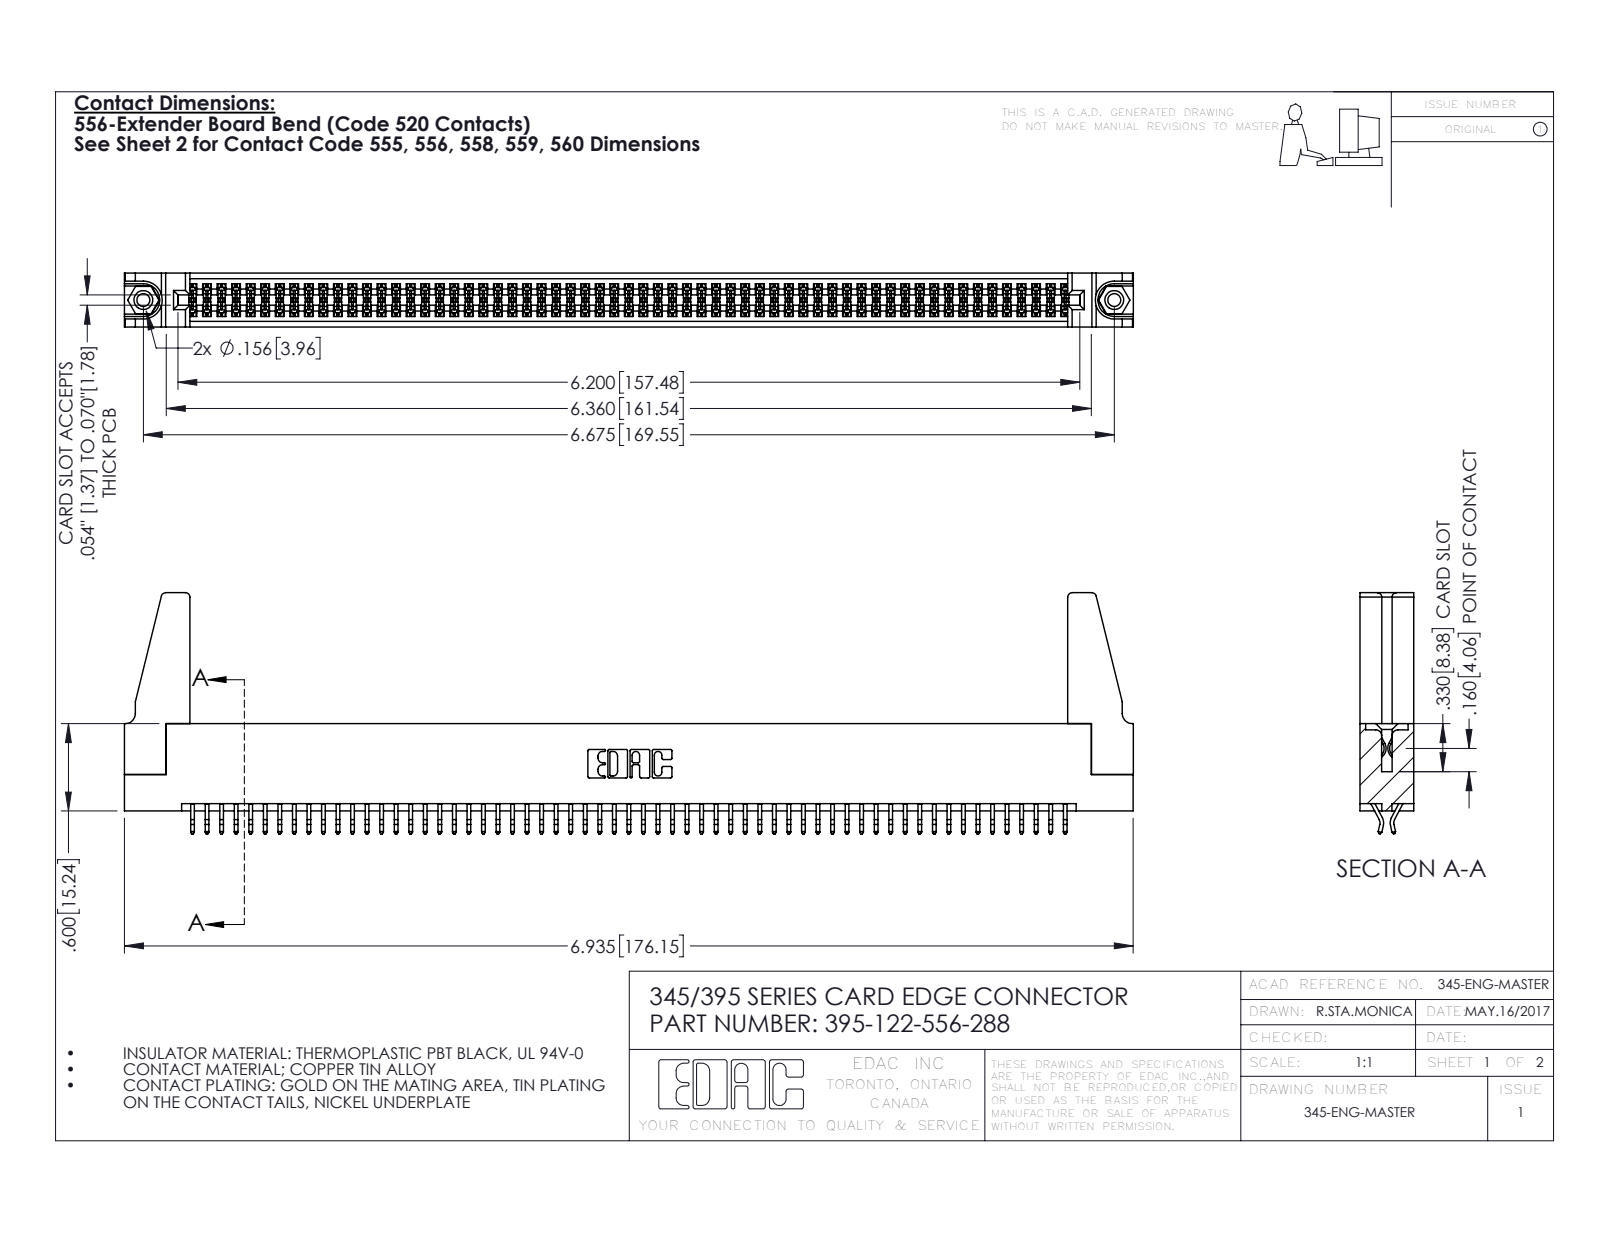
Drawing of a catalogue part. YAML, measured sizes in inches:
part_name: "345-292-001_556 Tail; 395-122-556-288; 345-220-078_345-220-088; 345 Part_Flush Mounting Lugs - 0.156 Dia-TH (+1 more)"
step_written_by: "SolidWorks 2016 (CONFIG_CONTROL_DESIGN)"
units: inches
bodies: {solids: 127, faces: 7082, planar: 4666, cylindrical: 2400, other: 16}
overall_size: [6.936, 1.657, 0.37]
volume: 1.253
surface_area: 44.85
round_holes:
  - {diameter: 0.089, count: 2}
  - {diameter: 0.125, count: 2}
  - {diameter: 0.156, count: 2}
  - {diameter: 0.064, count: 1}
round_bosses_or_shafts:
  - {diameter: 0.155, count: 2}
partial_cylinders:
  - {radius: 0.006, count: 183}
  - {radius: 0.01, count: 22}
  - {radius: 0.03, count: 8}
  - {radius: 0.007, count: 6}
  - {radius: 0.031, count: 6}
  - {radius: 0.026, count: 3}
  - {radius: 0.01, count: 2}
  - {radius: 0.014, count: 2}
face_to_face_distances: [0.072, 0.298, 0.37, 0.2, 0.025, 0.098, 0.272, 0.225, 0.175, 0.149]
hole_center_spacings: [0.27, 6.439, 6.675]
